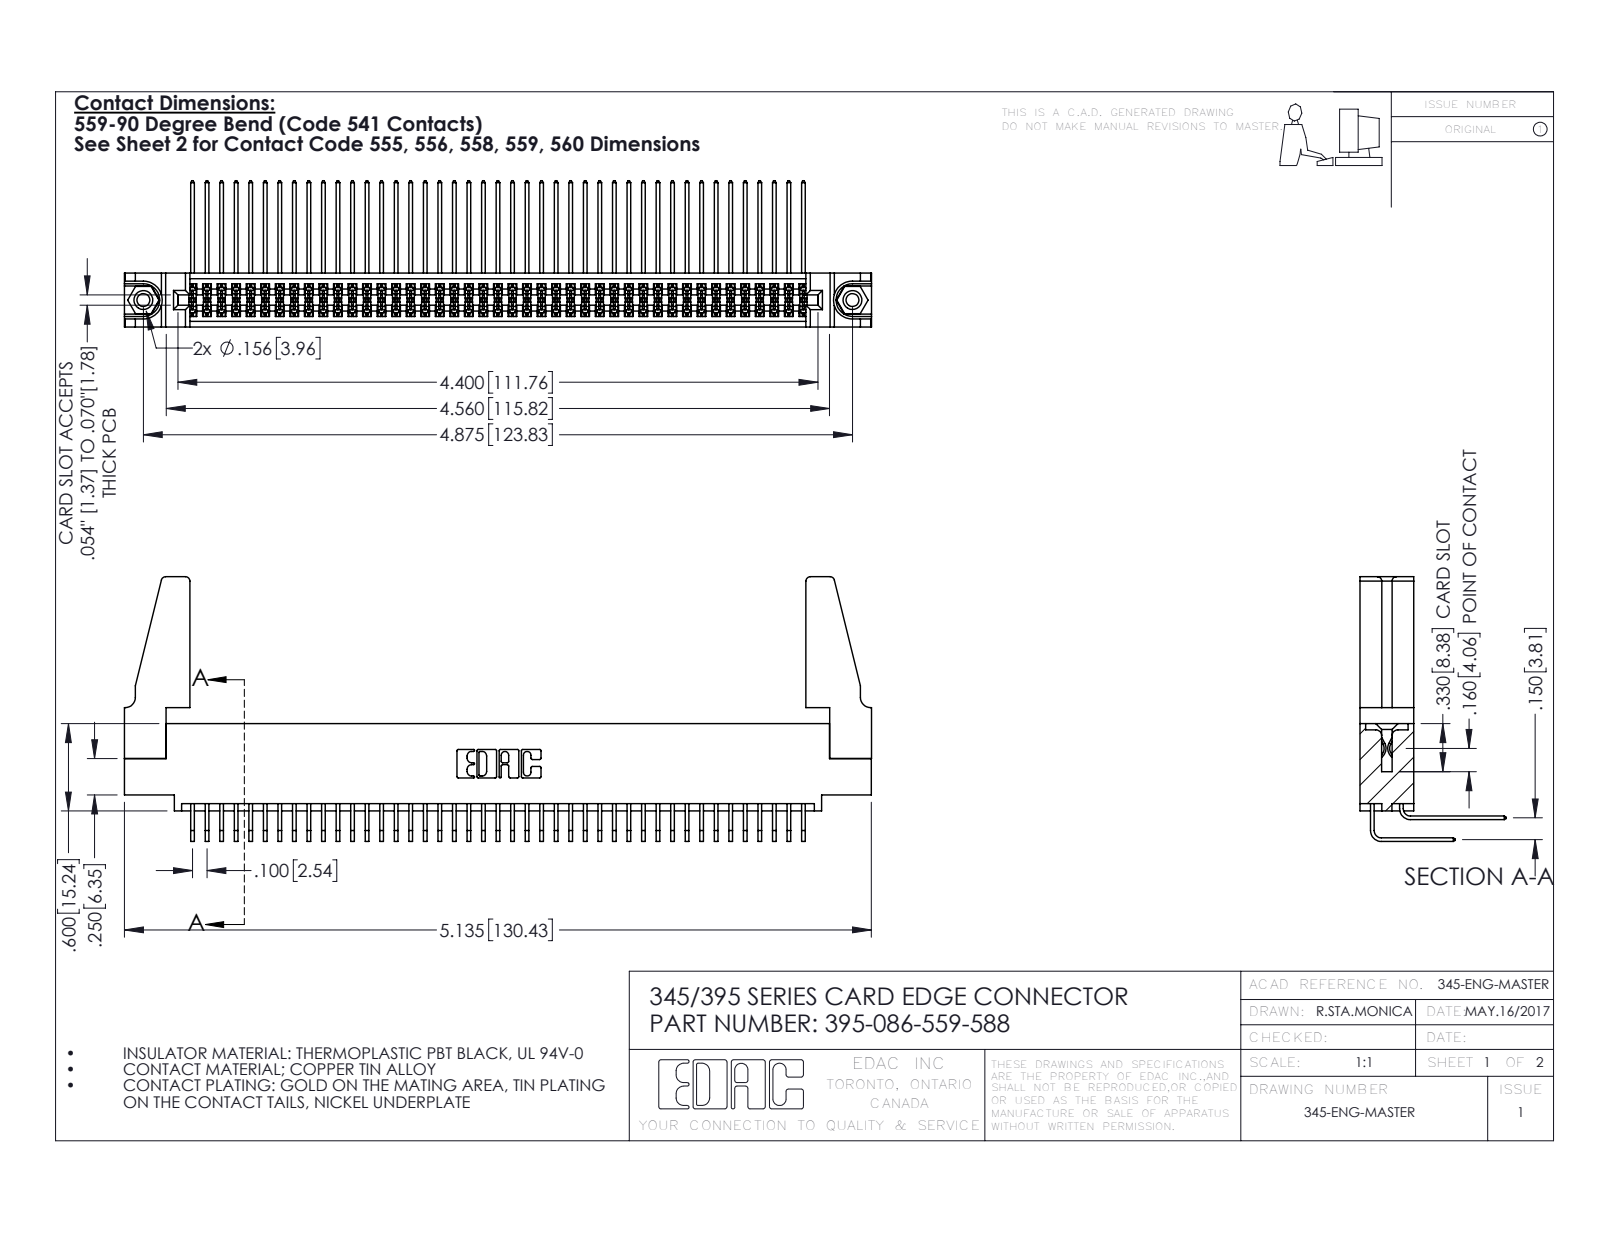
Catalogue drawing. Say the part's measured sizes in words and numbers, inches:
The part is named "345-292-001_558 559 Tail - 1; 345-220-078_345-220-088; 345-292-001_559 Tail - 2; 395-086-559-588 (+2 more)". Its 3-D file was written by "SolidWorks 2016 (CONFIG_CONTROL_DESIGN)". It is 91 solids with 4726 faces: 3166 planar, 1544 cylindrical and 16 other. Overall it measures 5.136 by 1.819 by 1.005 inches. Its volume is 0.998 cubic inches and its surface area 38.65 square inches. Round holes: 2 of diameter 0.089, 2 of diameter 0.125, 2 of diameter 0.156, 1 of diameter 0.064. Round bosses or shafts: 2 of diameter 0.155. Partial cylindrical surfaces (rounded edges, fillets, slot ends): 129 of radius 0.006, 22 of radius 0.01, 8 of radius 0.03, 6 of radius 0.007, 6 of radius 0.031, 3 of radius 0.026, 2 of radius 0.014, 2 of radius 0.019. The main face-to-face distances are 0.072, 0.298, 0.37, 0.2, 0.098, 0.272, 0.025, 0.225, 0.175, 0.15. The hole center spacings are 0.27, 4.639, 4.875.
